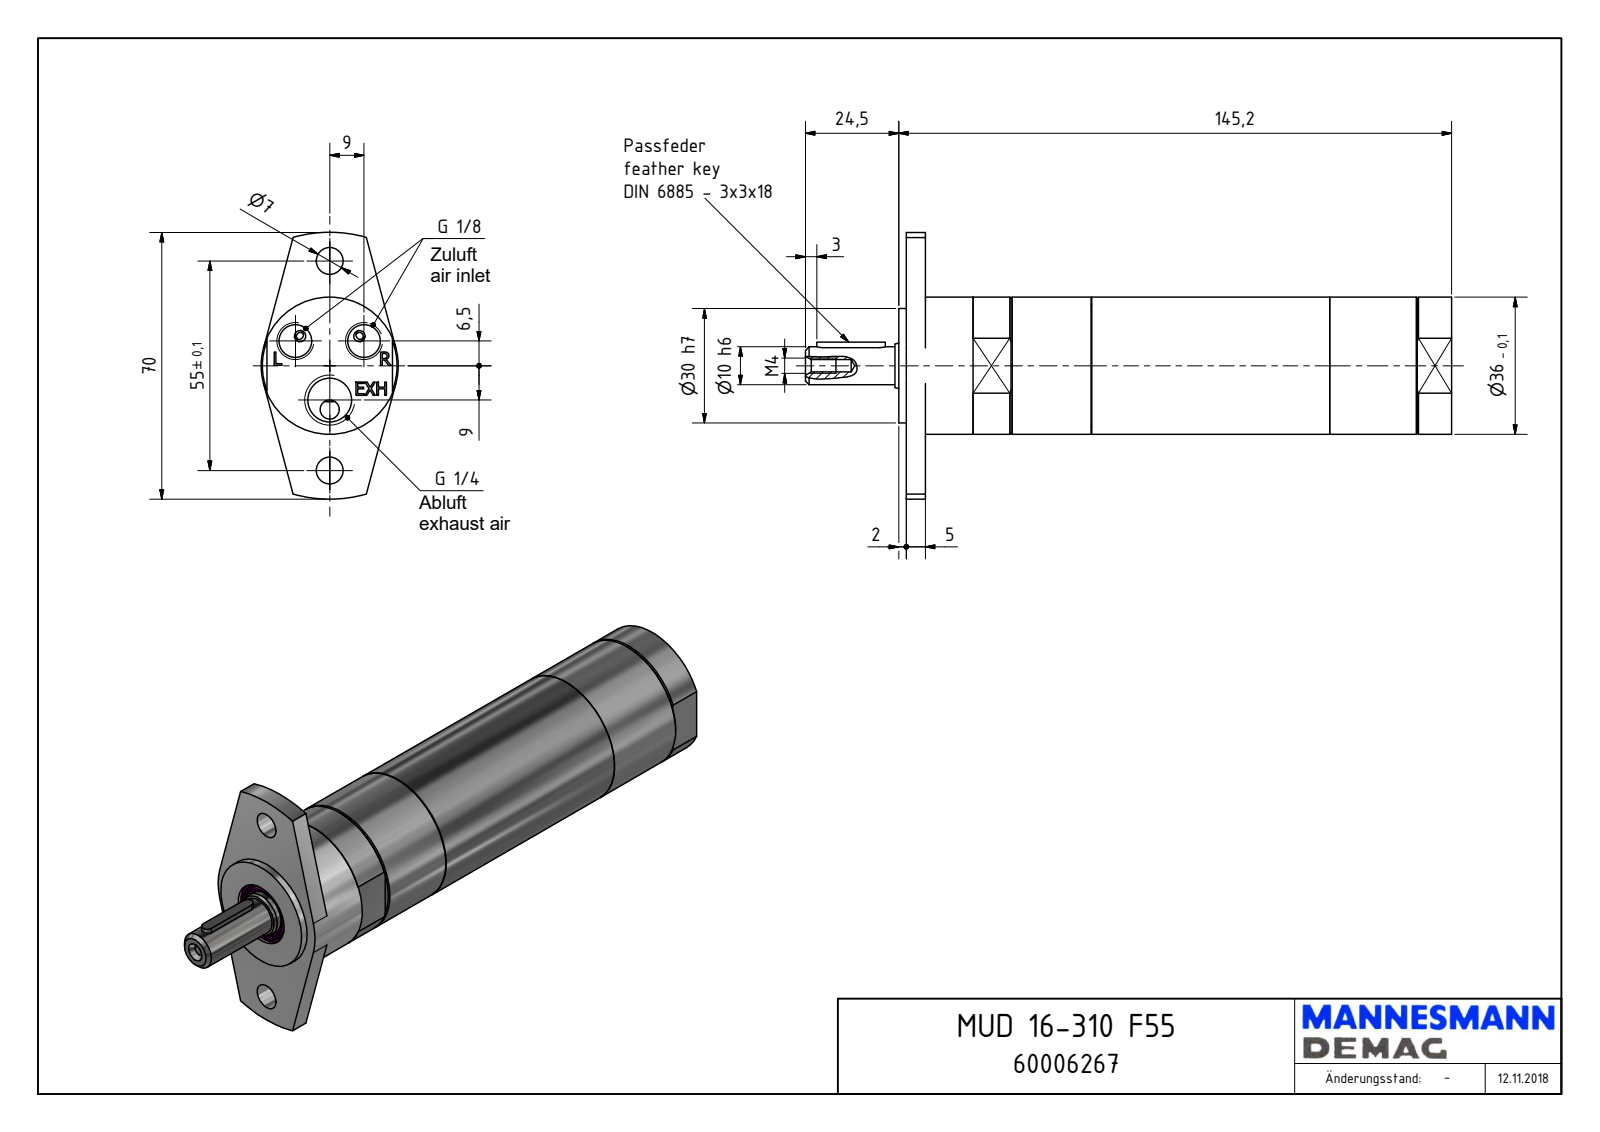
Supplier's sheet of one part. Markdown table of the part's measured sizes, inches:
| quantity | value |
| --- | --- |
| part name | MUD 16-310 F55_60006267 |
| STEP written by | Autodesk Inventor 2018 (AUTOMOTIVE_DESIGN) |
| units | inches |
| bodies | 1 solid, 138 faces (90 planar, 24 cylindrical, 24 other) |
| overall size | 6.681 × 2.756 × 1.417 |
| volume | 9.167 in³ |
| surface area | 35.99 in² |
| round holes (diameter × count) | 0.276 × 2, 0.337 × 2, 0.128 × 1, 0.451 × 1, 0.61 × 1, 0.669 × 1 |
| round bosses / shafts (diameter × count) | 1.417 × 1, 1.26 × 1, 1.181 × 1, 0.47 × 1, 0.394 × 1 |
| partial cylindrical surfaces (radius × count) | 0.059 × 2, 1.378 × 1 |
| main face-to-face distances | 0.197, 5.638, 5.441, 0.079, 0.276, 5.717, 1.299, 5.314, 5.235, 5.038 |
| hole center spacings | 0.437, 0.706, 0.9, 1.083, 1.385, 0.354, 0.709, 0.728 |
